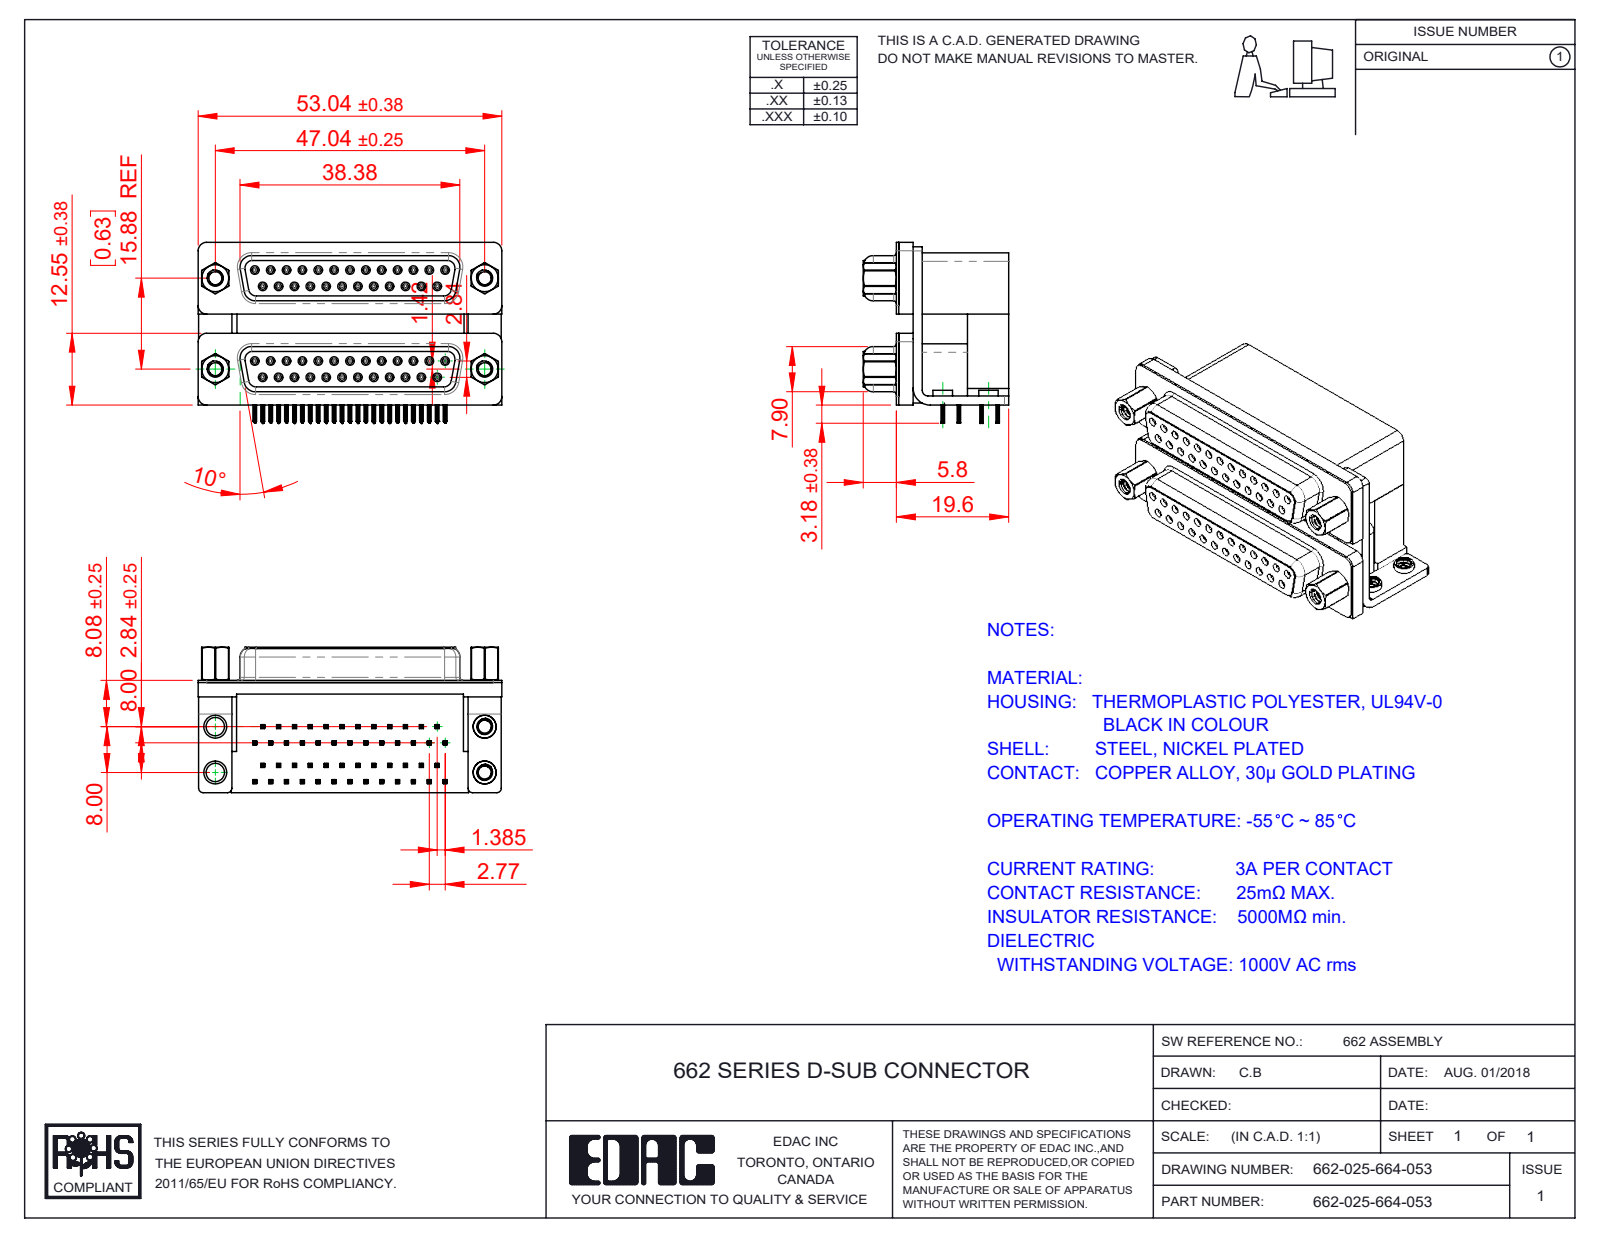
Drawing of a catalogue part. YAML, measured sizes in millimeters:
part_name: "662 Housing Upper_25 Contacts L; 662 Contact Top Lower; 662 4-40 Threaded Board Mount; 662 Housing Spacer_25 Contacts L (+8 more)"
step_written_by: "SolidWorks 2020 (CONFIG_CONTROL_DESIGN)"
units: millimeters
bodies: {solids: 69, faces: 8184, planar: 3632, cylindrical: 2024, other: 2528}
overall_size: [53.04, 31.61, 25.4]
volume: 23358
surface_area: 26205
round_holes:
  - {diameter: 0.8, count: 50}
  - {diameter: 0.9, count: 50}
  - {diameter: 2.26, count: 8}
  - {diameter: 2.29, count: 4}
  - {diameter: 2.75, count: 4}
  - {diameter: 3.2, count: 4}
  - {diameter: 3.5, count: 4}
  - {diameter: 4, count: 4}
  - {diameter: 4.8, count: 4}
  - {diameter: 5, count: 4}
round_bosses_or_shafts:
  - {diameter: 1.2, count: 50}
  - {diameter: 4.9, count: 4}
  - {diameter: 4.75, count: 4}
  - {diameter: 4, count: 4}
  - {diameter: 3.9, count: 4}
  - {diameter: 3.4, count: 4}
  - {diameter: 2.79, count: 4}
partial_cylinders:
  - {radius: 0.1, count: 400}
  - {radius: 0.15, count: 200}
  - {radius: 0.35, count: 100}
  - {radius: 0.34, count: 50}
  - {radius: 0.28, count: 24}
  - {radius: 1.35, count: 18}
  - {radius: 1.5, count: 13}
  - {radius: 0.5, count: 8}
face_to_face_distances: [15.88, 0.4, 19.2, 7.2, 12, 10.7, 6.2, 2.9, 16.7, 9.5]
hole_center_spacings: [3.16, 2.77, 5.54, 11.08, 8.31, 5.03, 13.85, 7.48]
